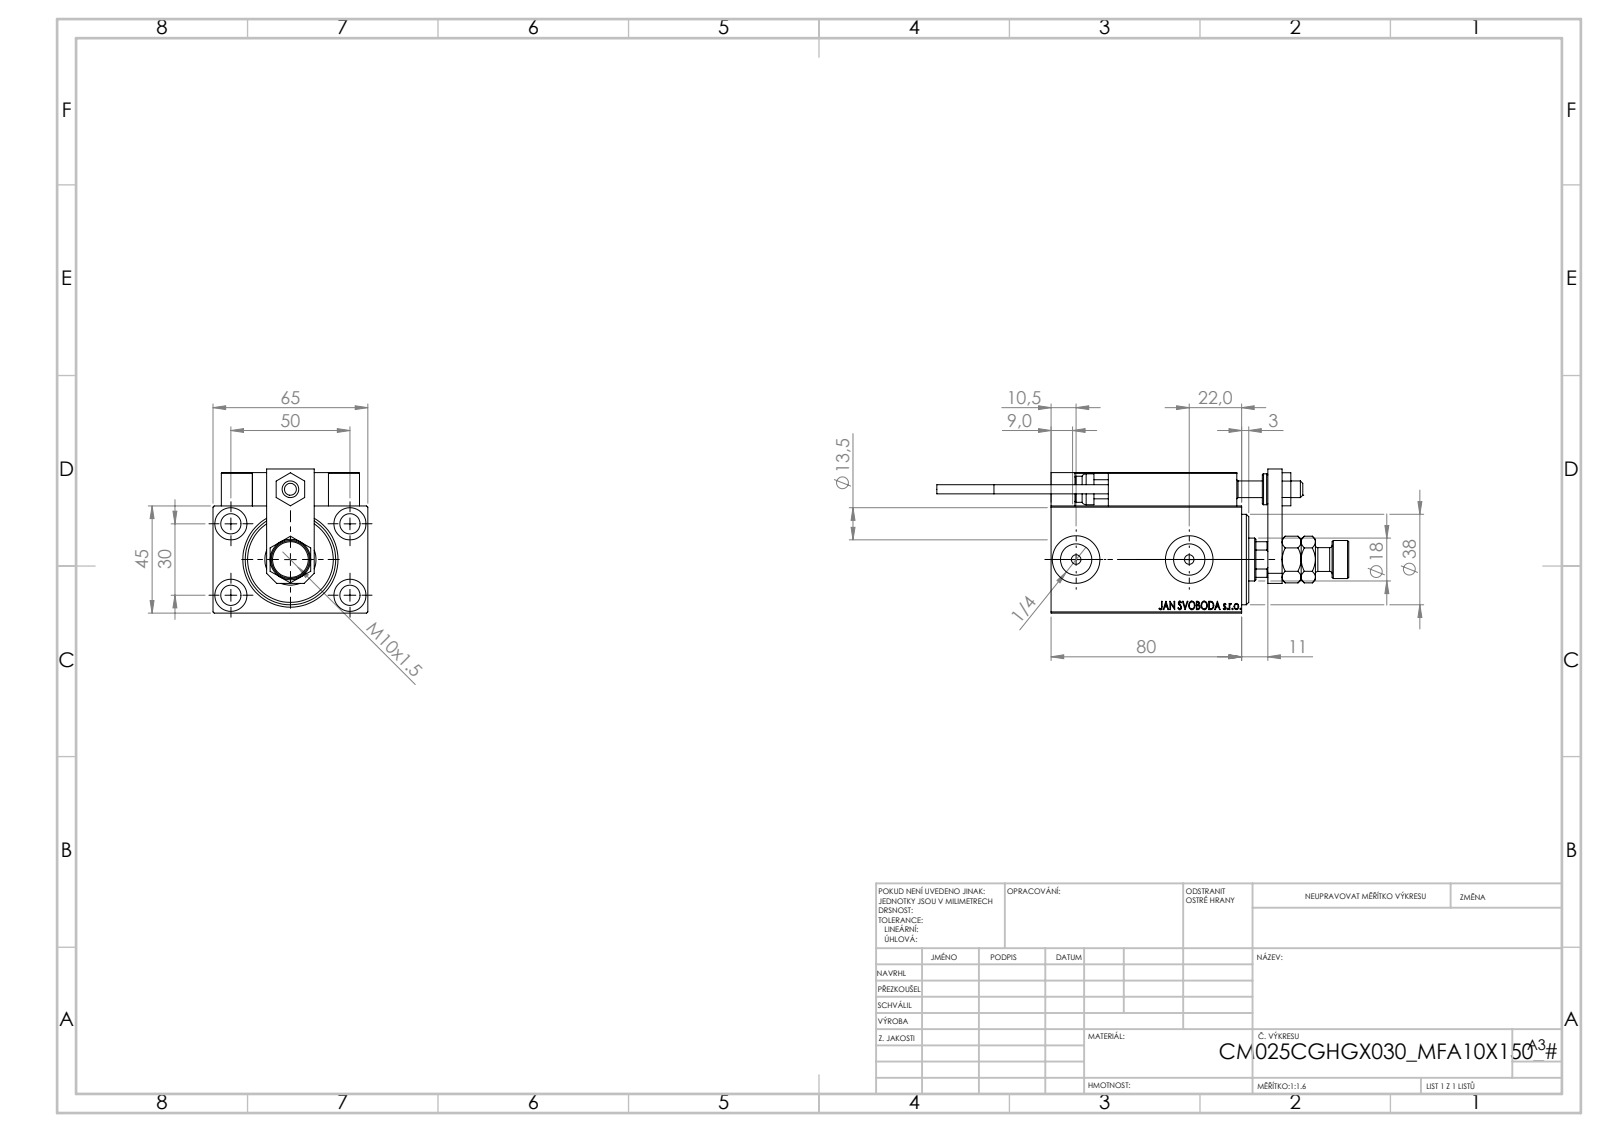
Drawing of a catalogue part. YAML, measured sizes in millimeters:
part_name: "X_Y_MFA; TYC_L79; KONCOVKA; SWITCH_X_FRONT_BACK (+8 more)"
step_written_by: "SolidWorks 2019 (CONFIG_CONTROL_DESIGN)"
units: millimeters
bodies: {solids: 24, faces: 1334, planar: 576, cylindrical: 192, other: 566}
overall_size: [173, 65, 60.5]
volume: 253650
surface_area: 76114
round_holes:
  - {diameter: 4, count: 6}
  - {diameter: 8, count: 5}
  - {diameter: 8.5, count: 5}
  - {diameter: 3.2, count: 4}
  - {diameter: 13.5, count: 4}
  - {diameter: 5, count: 2}
  - {diameter: 13.16, count: 2}
  - {diameter: 20, count: 2}
  - {diameter: 7, count: 1}
  - {diameter: 14.5, count: 1}
  - {diameter: 18, count: 1}
  - {diameter: 21.5, count: 1}
round_bosses_or_shafts:
  - {diameter: 5, count: 2}
  - {diameter: 3.8, count: 2}
  - {diameter: 16, count: 1}
  - {diameter: 13, count: 1}
  - {diameter: 11, count: 1}
  - {diameter: 10, count: 1}
partial_cylinders:
  - {radius: 0.3, count: 30}
  - {radius: 3, count: 2}
  - {radius: 8.5, count: 1}
face_to_face_distances: [45, 14, 65, 59, 6, 3, 91, 13, 3.5, 5]
hole_center_spacings: [29.15, 11.37, 20, 28.9, 29.59, 29.69, 30, 32.06]
